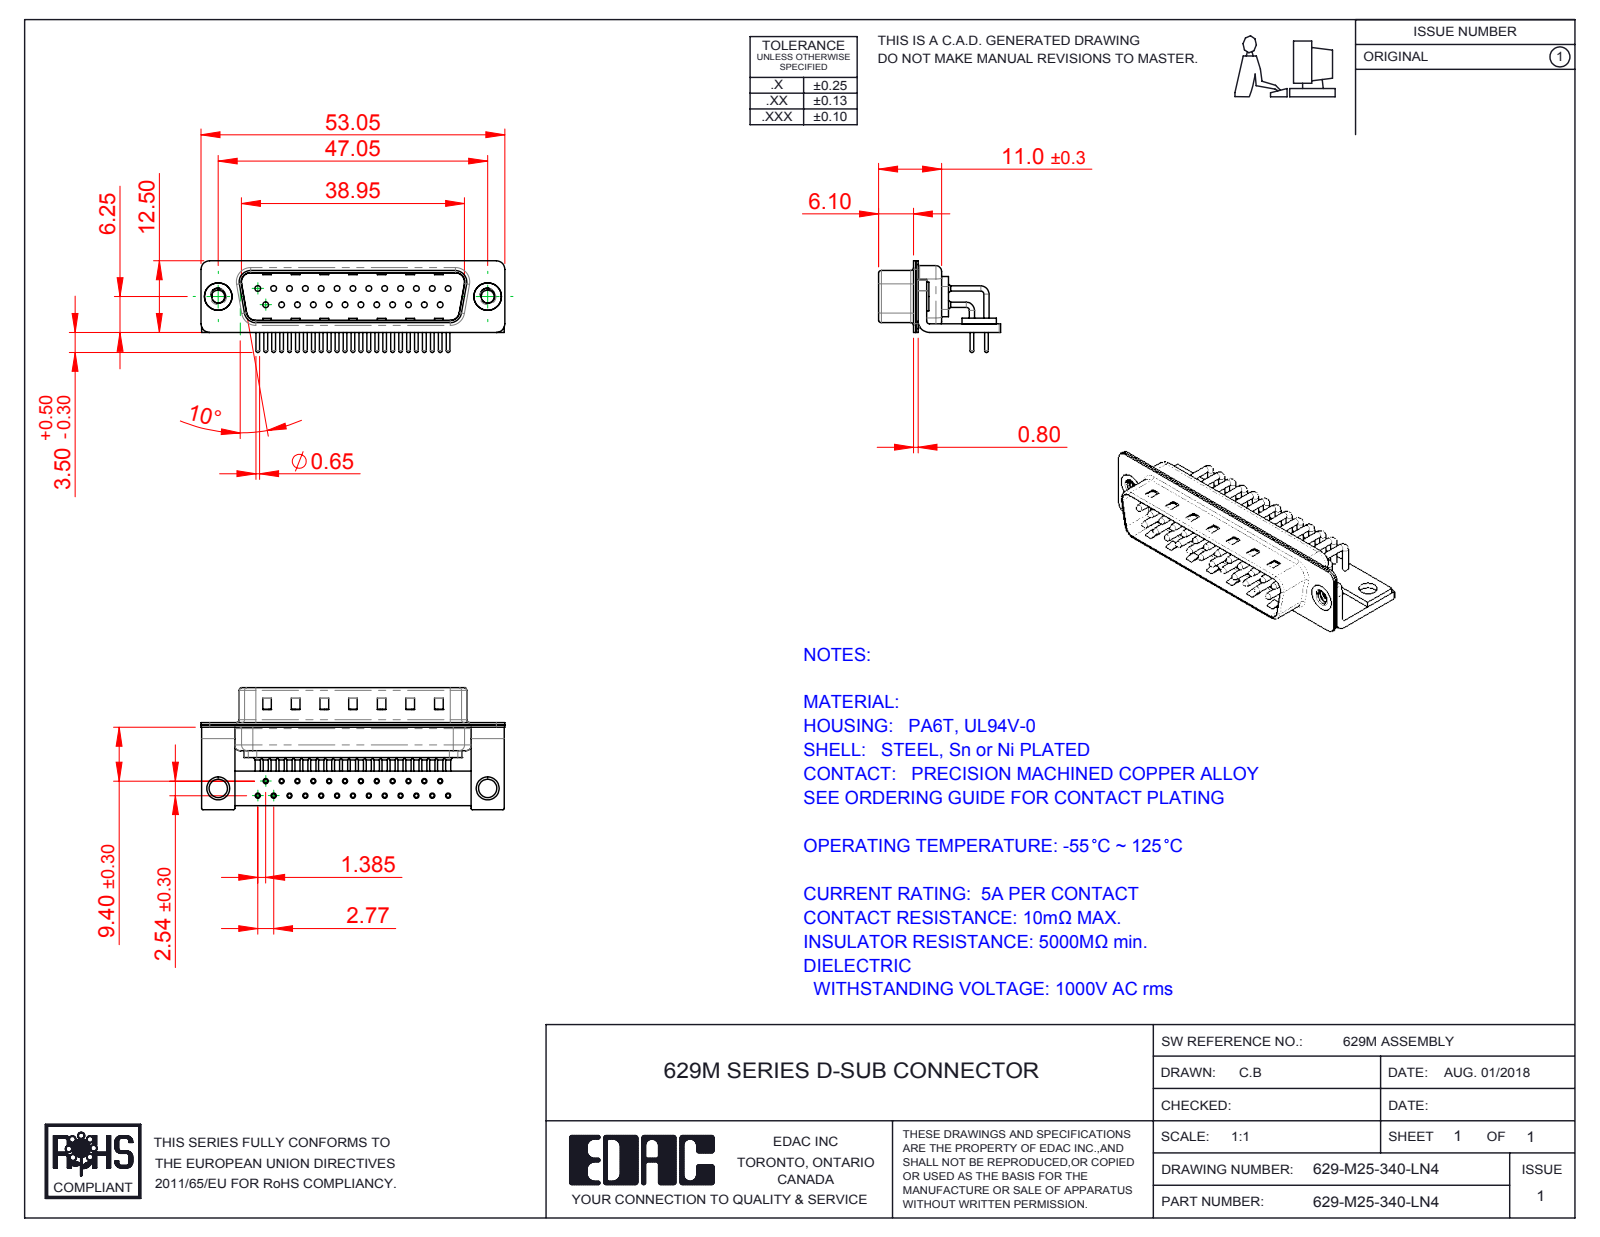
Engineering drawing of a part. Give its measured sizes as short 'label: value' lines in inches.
name: 629M Housing_25 Contacts; 629M Shell Front_25 Contacts; 629M Shell Rear_25 Contacts; 629M Contact Row 1 (+5 more)
written by: SolidWorks 2016 (CONFIG_CONTROL_DESIGN)
unit: in
bodies: 33 solids, 3226 faces (1797 planar, 1109 cylindrical, 320 other)
size: 2.089 × 0.839 × 0.63
volume: 0.211 in³; area: 14.14 in²
holes: 25× ⌀0.035, 25× ⌀0.039, 25× ⌀0.067, 25× ⌀0.079, 2× ⌀0.089, 2× ⌀0.126, 2× ⌀0.157, 2× ⌀0.189
bosses: 25× ⌀0.059, 25× ⌀0.035, 25× ⌀0.026, 2× ⌀0.197, 2× ⌀0.193
rounds: 25× R0.04, 16× R0.01, 16× R0.059, 13× R0.079, 9× R0.02, 8× R0.063, 4× R0.024, 4× R0.026
face distances: 0.016, 0.033, 0.049, 0.059, 0.031, 0.376, 0.409, 0.039, 0.075, 0.327
hole spacings: 0.109, 0.218, 0.327, 0.436, 0.545, 0.124, 0.192, 0.654
